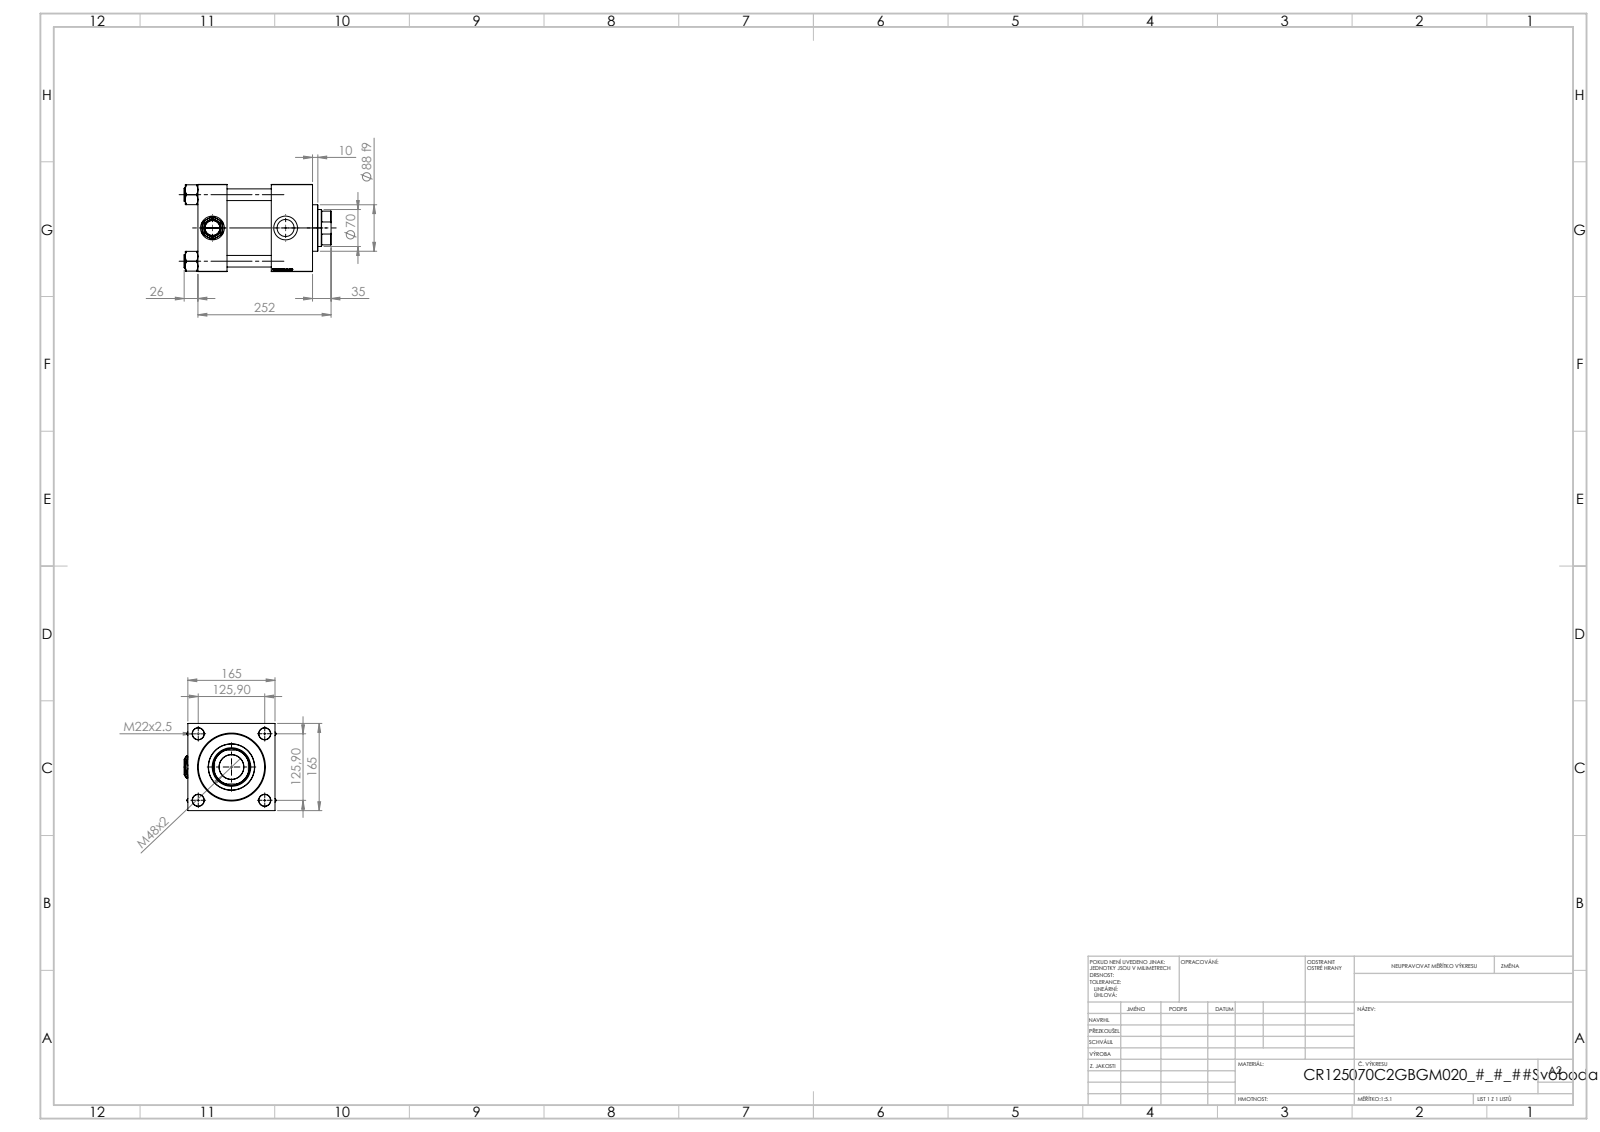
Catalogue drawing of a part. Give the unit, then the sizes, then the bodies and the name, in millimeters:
Units: millimetres
Overall size (bounding box): 278 × 174.07 × 165
Round holes (diameter × count): ⌀22 ×4, ⌀7 ×2, ⌀32.24 ×2, ⌀45 ×2, ⌀46.5 ×1, ⌀70 ×1, ⌀73 ×1, ⌀96 ×1, ⌀125 ×1, ⌀125.5 ×1
Round bosses / shafts (diameter × count): ⌀25 ×4, ⌀131 ×1, ⌀88 ×1
Partial cylindrical surfaces — rounded edges, fillets, slot ends (radius × count): R34 ×1
Main face-to-face distances: 165, 55, 162, 217, 78, 139, 84, 188.3, 133.3, 49.3
Hole centre spacings: 89.02, 125.9, 178.05, 138.5
Volume: 4 600 000 mm³ · Surface area: 516 903 mm²
Bodies: 12 solids, 1250 faces (598 planar, 94 cylindrical, 558 other)
Part name (STEP PRODUCT): V215CR_C_TYCINKA; Zatka_pro_OIL_PORT; V215CR_C_Body; V215CR_VCP_C (+2 more)
STEP written by: SolidWorks 2019 (CONFIG_CONTROL_DESIGN)
